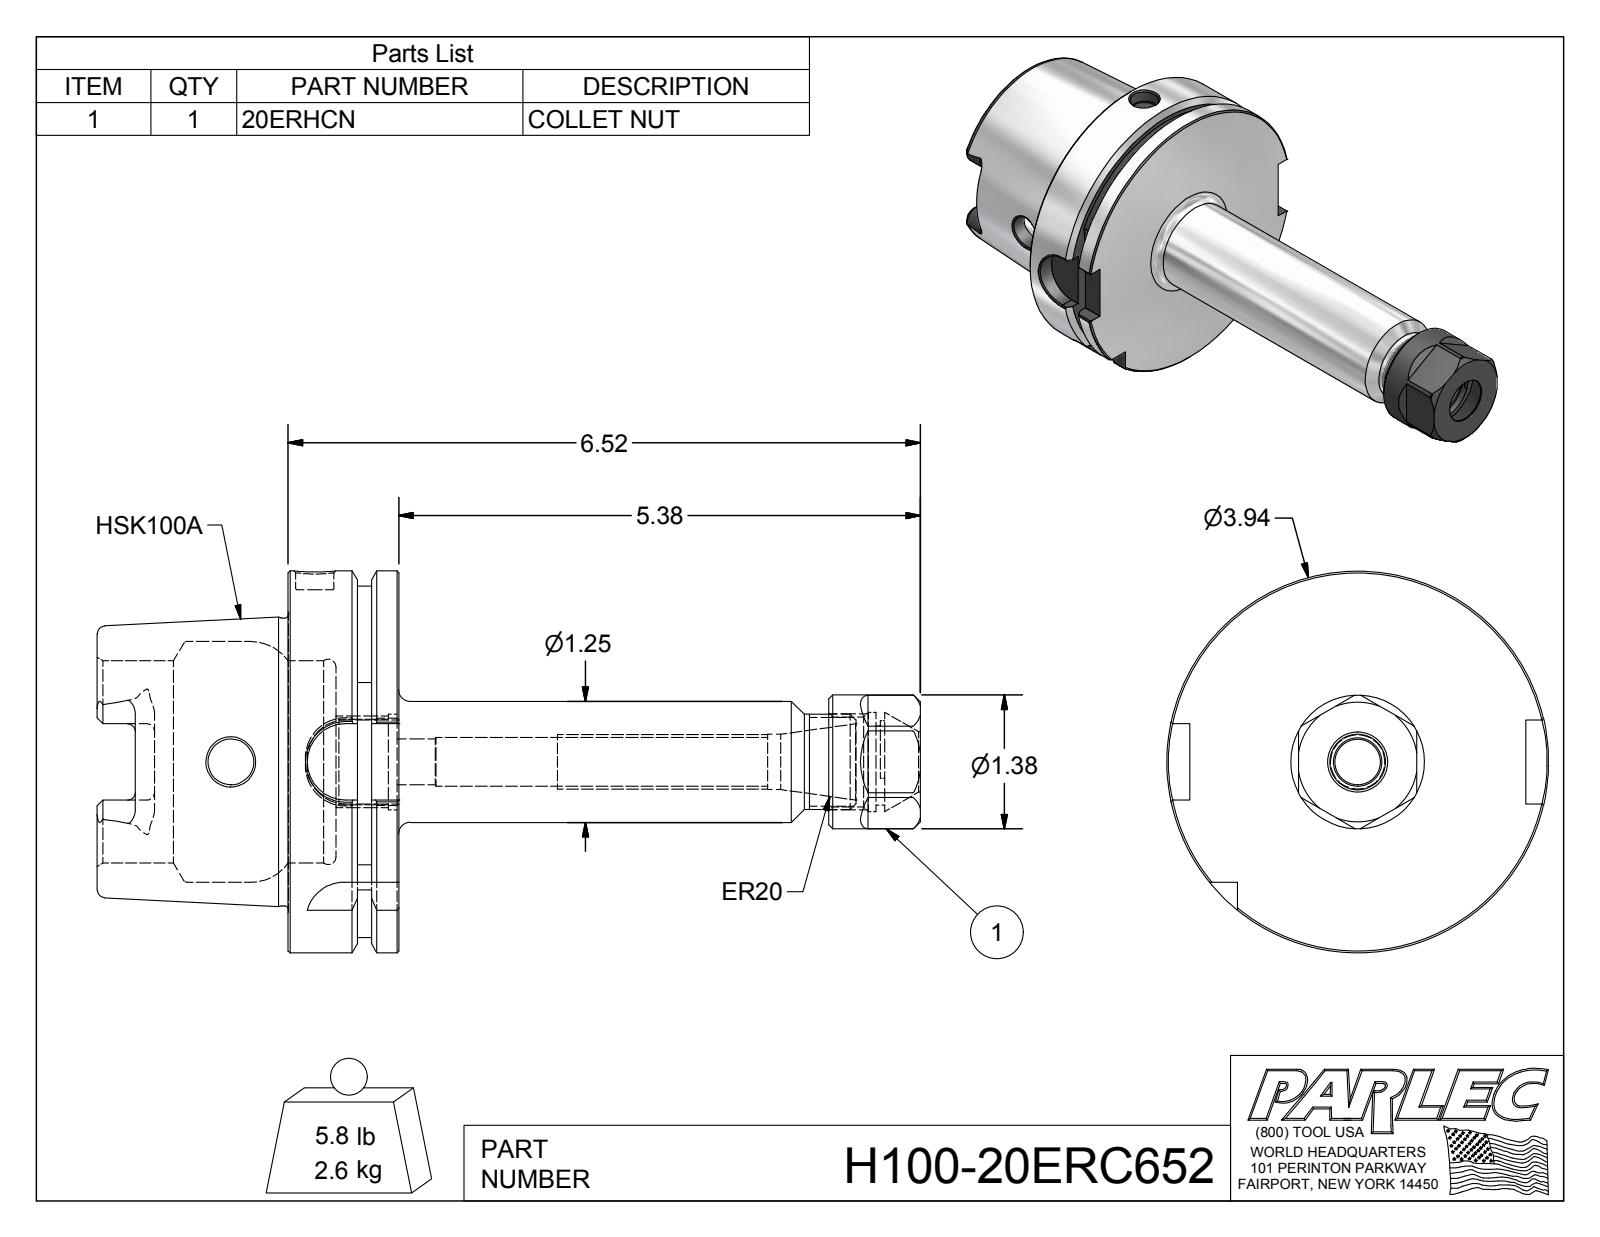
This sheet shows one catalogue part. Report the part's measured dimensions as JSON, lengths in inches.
{"part_name": "H100-20ERC652; H100-20ER6-1; 20ERHCN", "step_written_by": "Autodesk Inventor 2012 (AUTOMOTIVE_DESIGN)", "units": "inches", "bodies": {"solids": 2, "faces": 169, "planar": 61, "cylindrical": 42, "other": 66}, "overall_size": [8.489, 3.937, 3.937], "volume_in3": 20.63, "surface_area_in2": 111.4, "round_holes": [[0.472, 2], [0.394, 1], [0.472, 1], [0.502, 1], [0.57, 1], [0.62, 1], [0.82, 1], [0.881, 1], [0.925, 1], [0.985, 1], [1.024, 1], [2.087, 1]], "round_bosses_or_shafts": [[3.937, 1], [2.967, 1], [1.378, 1], [1.25, 1], [0.984, 1]], "partial_cylinders_radius": [[0.079, 6], [0.192, 4], [0.394, 4], [0.423, 1], [1.811, 1]], "face_to_face_distances": [1.142, 0.492, 0.65, 1.969, 2.461, 3.11, 1.122, 1.22, 5.378, 2.83], "hole_center_spacings": [0.037]}
